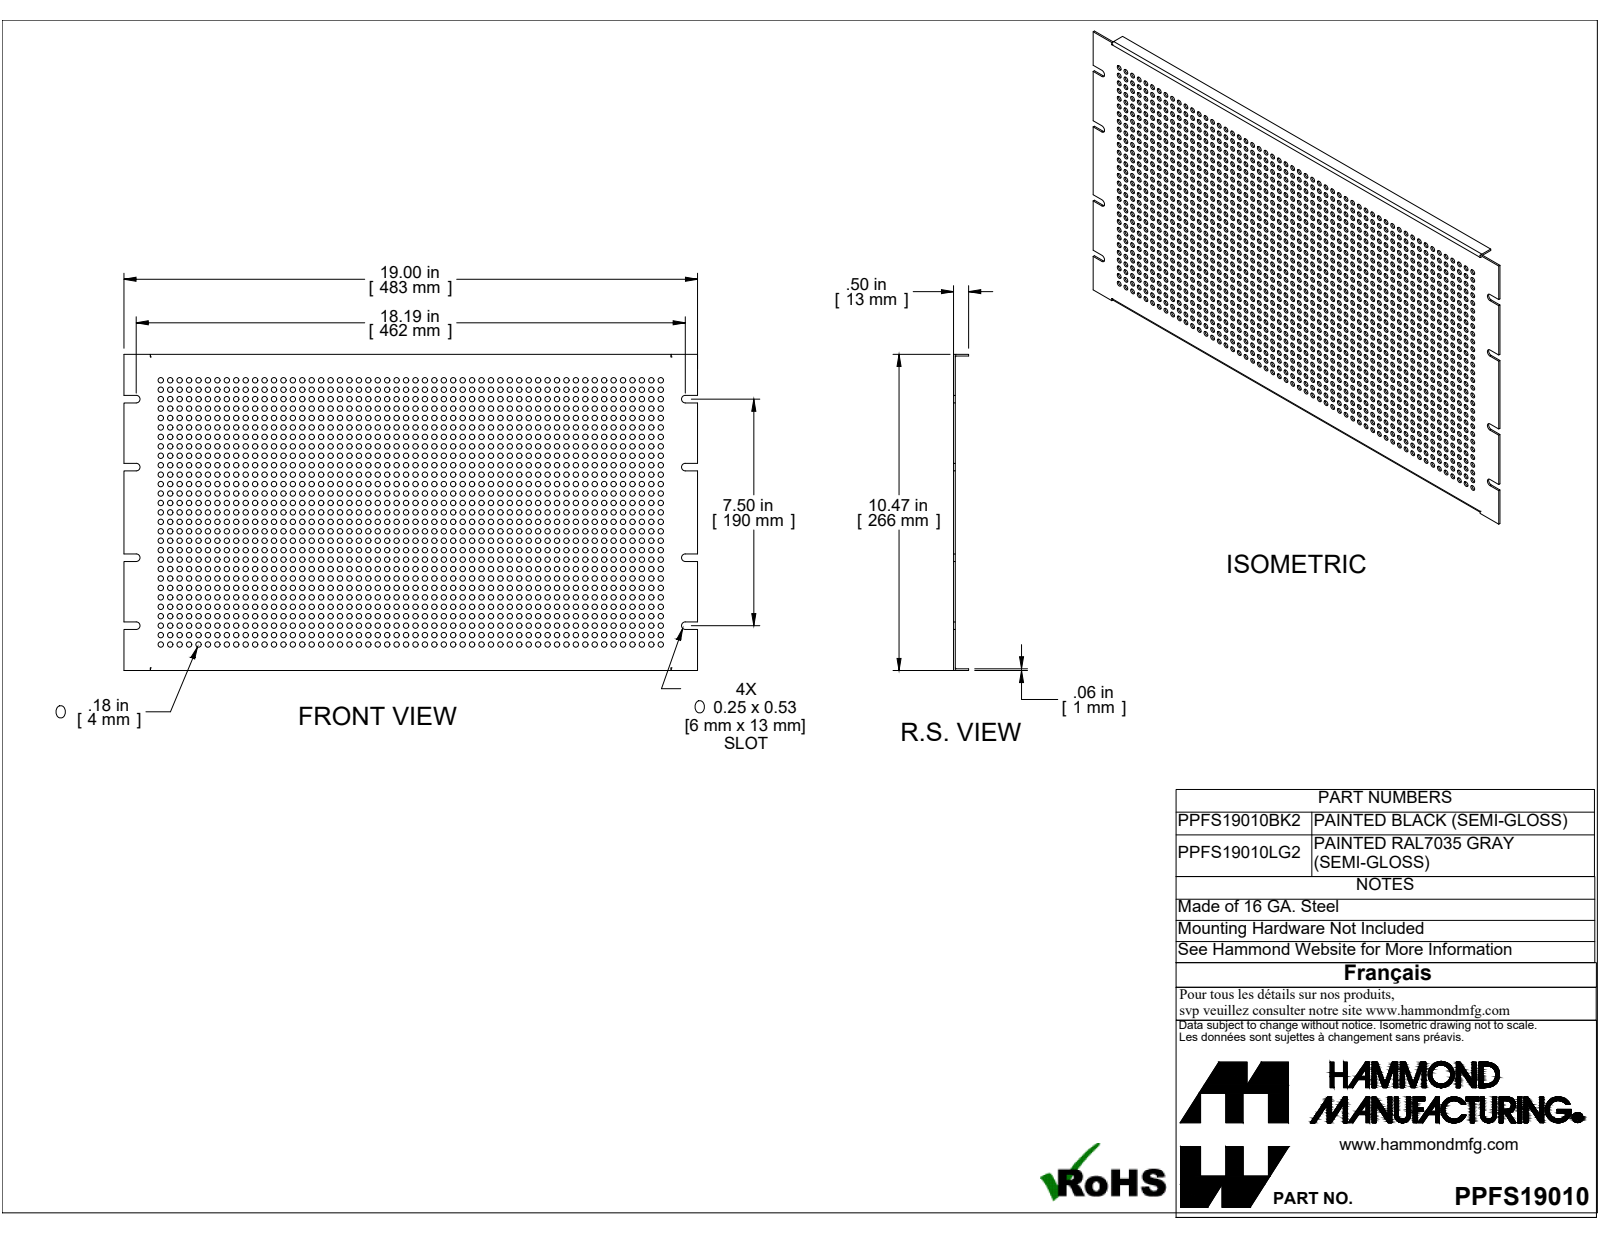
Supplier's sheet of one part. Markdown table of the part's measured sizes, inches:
| quantity | value |
| --- | --- |
| part name | PPFS19010LG2 |
| STEP written by | SolidWorks 2019 (CONFIG_CONTROL_DESIGN) |
| units | inches |
| bodies | 1 solid, 1628 faces (50 planar, 1578 cylindrical, 0 other) |
| overall size | 19 × 10.468 × 0.5 |
| volume | 9.906 in³ |
| surface area | 401.1 in² |
| round holes (diameter × count) | 0.177 × 1566 |
| partial cylindrical surfaces (radius × count) | 0.125 × 8, 0.029 × 2, 0.086 × 2 |
| main face-to-face distances | 0.057, 0.057, 10.411, 10.468, 10.354, 0.5, 0.443, 19, 0.25, 2.25 |
| hole center spacings | 1.25, 0.313, 2.5, 0.937, 1.563, 3.75, 2.187, 2.813 |
